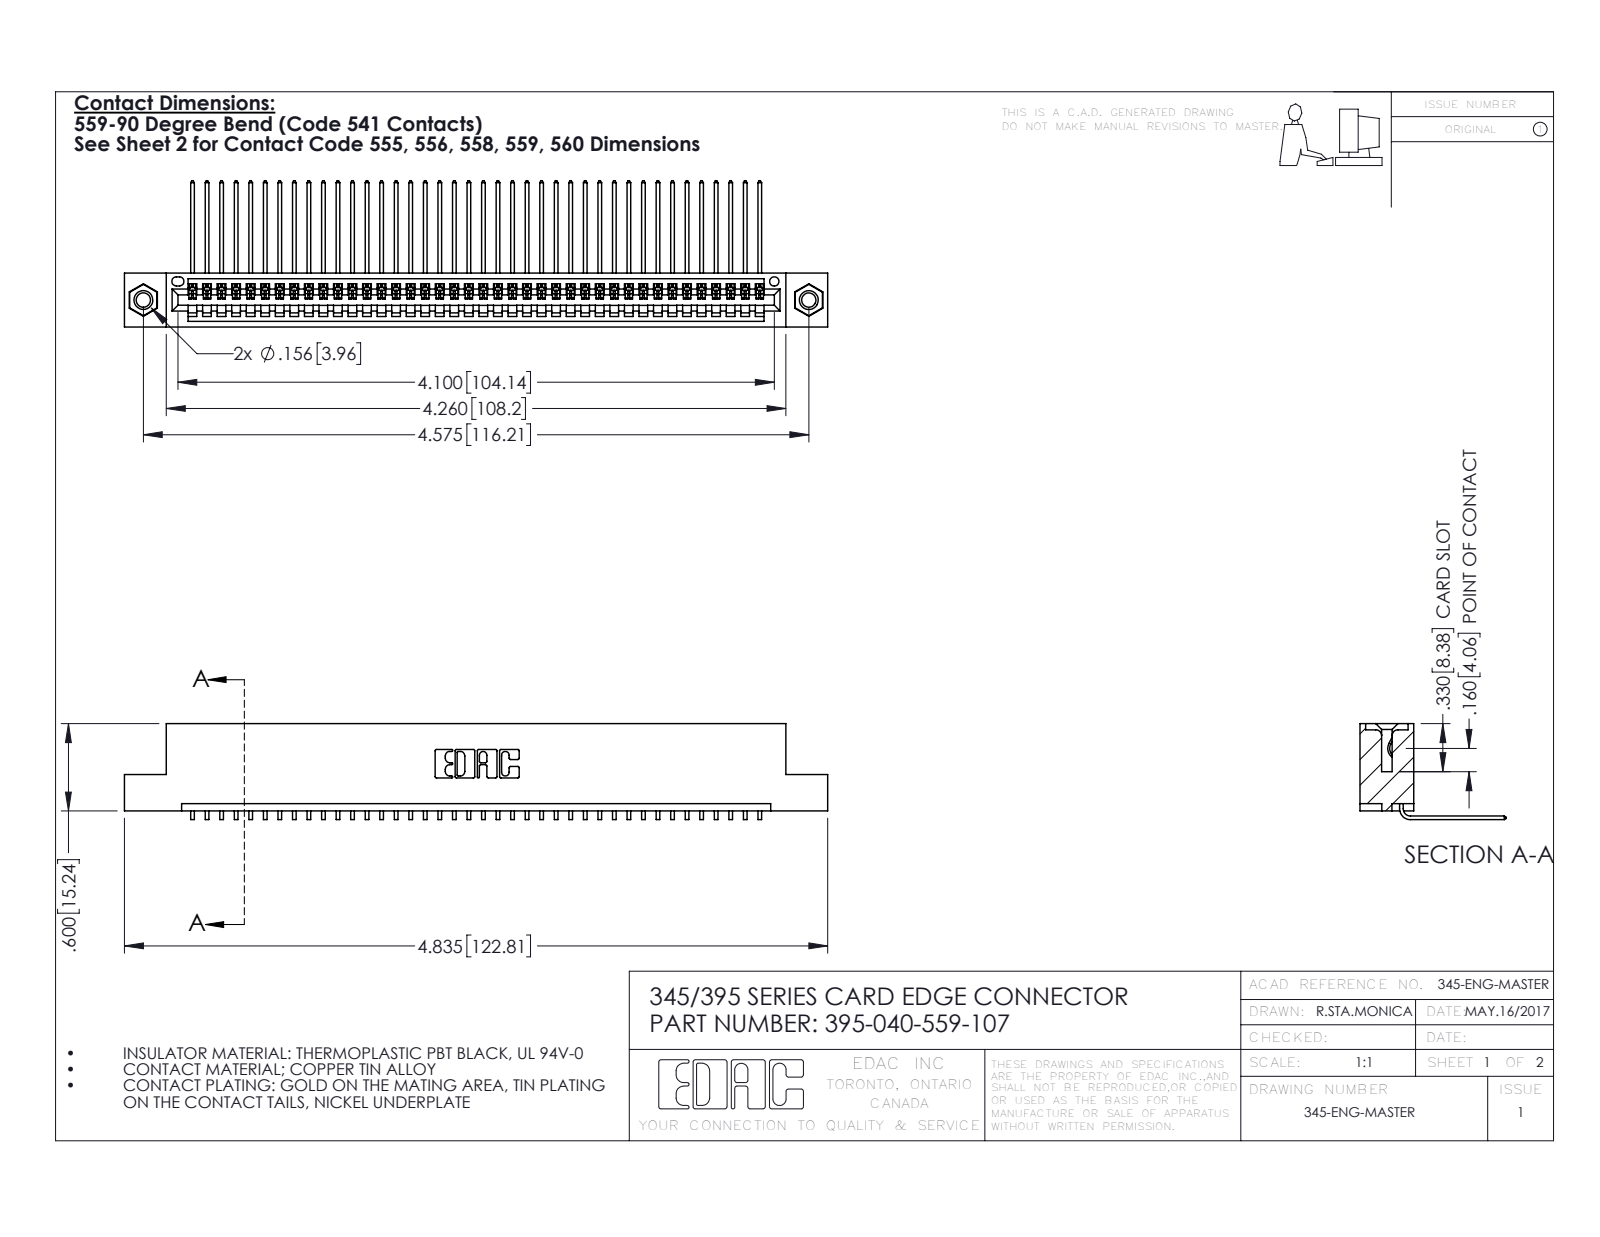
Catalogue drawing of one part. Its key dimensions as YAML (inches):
part_name: "345 Part_Flush Mounting Lugs - 0.156 Dia-TI; 395-040-559-107; 345-292-001_558 559 Tail - 1; 345-250-001_345-250-005-103"
step_written_by: "SolidWorks 2016 (CONFIG_CONTROL_DESIGN)"
units: inches
bodies: {solids: 43, faces: 2586, planar: 1792, cylindrical: 778, other: 16}
overall_size: [4.835, 1.005, 0.659]
volume: 0.718
surface_area: 25.46
round_holes:
  - {diameter: 0.098, count: 2}
  - {diameter: 0.125, count: 2}
  - {diameter: 0.156, count: 2}
  - {diameter: 0.064, count: 1}
round_bosses_or_shafts:
  - {diameter: 0.155, count: 2}
partial_cylinders:
  - {radius: 0.006, count: 80}
  - {radius: 0.01, count: 22}
  - {radius: 0.007, count: 6}
  - {radius: 0.031, count: 6}
  - {radius: 0.026, count: 3}
  - {radius: 0.031, count: 2}
  - {radius: 0.04, count: 2}
  - {radius: 0.014, count: 1}
face_to_face_distances: [0.072, 0.298, 0.37, 0.2, 0.098, 0.272, 0.025, 0.225, 0.149, 0.072]
hole_center_spacings: [0.27, 4.339, 4.575]
